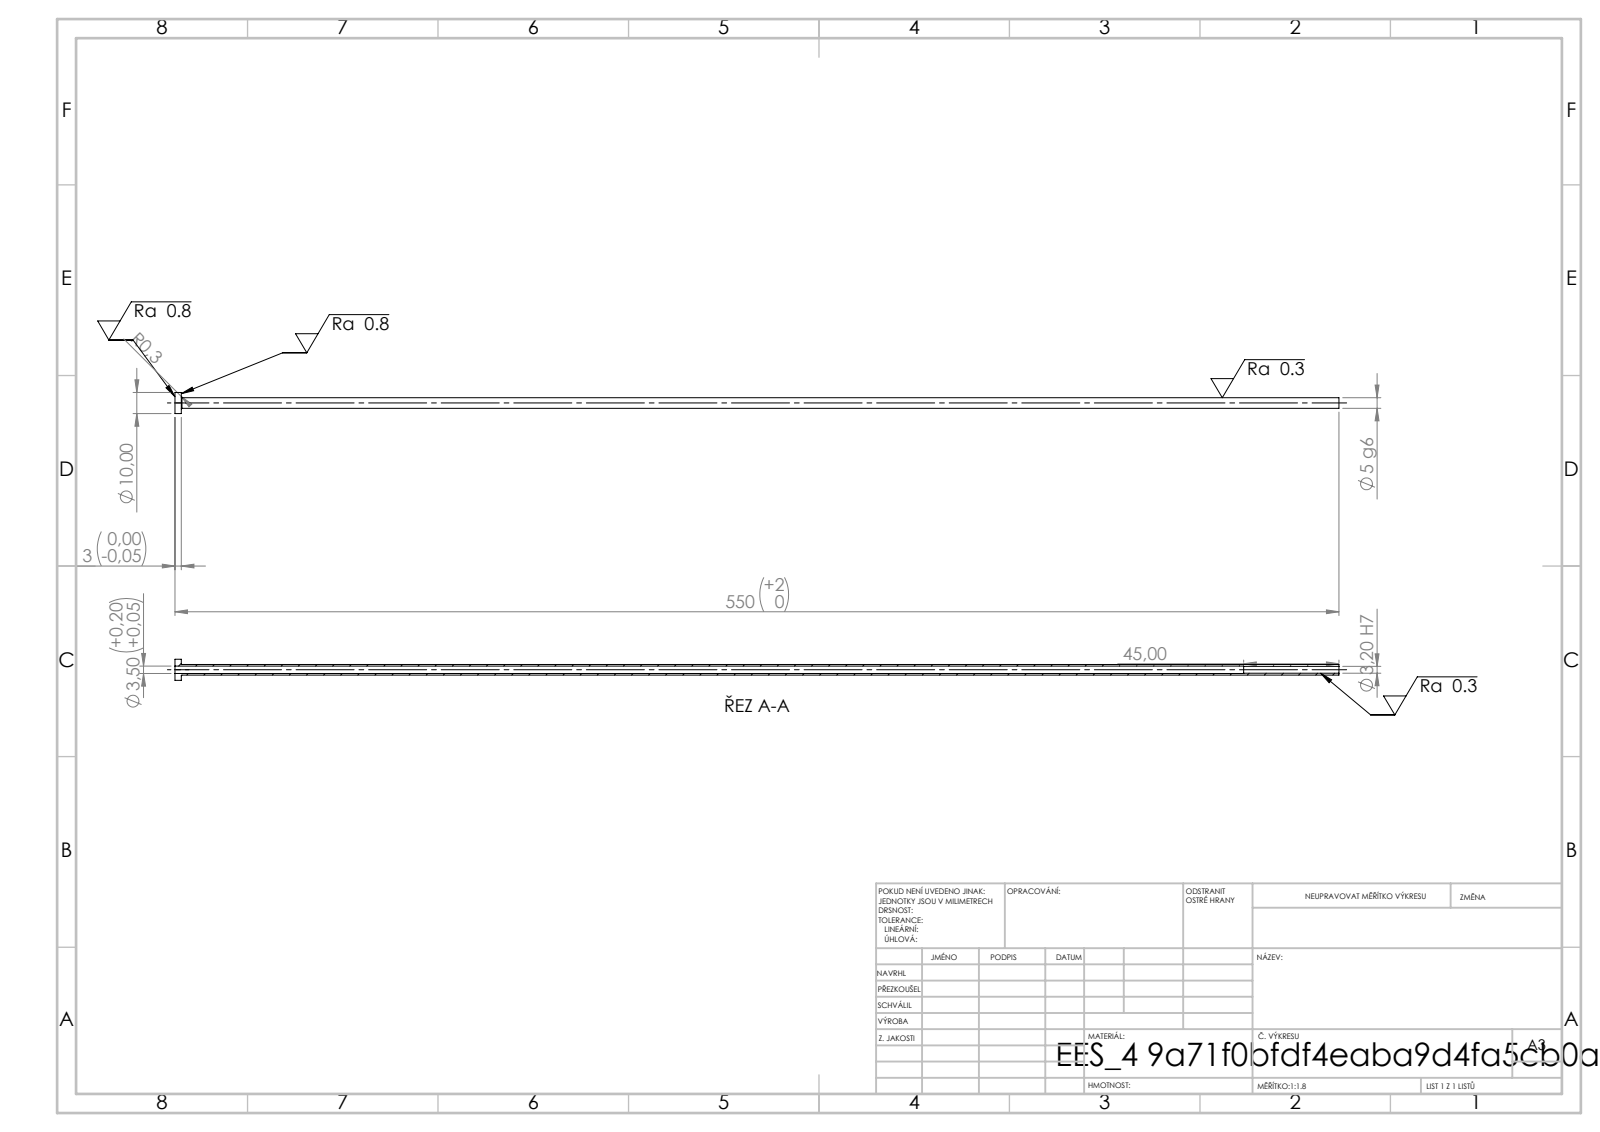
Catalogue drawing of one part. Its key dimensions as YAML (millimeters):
step_written_by: "SolidWorks 2019 (CONFIG_CONTROL_DESIGN)"
units: millimeters
bodies: {solids: 1, faces: 14, planar: 4, cylindrical: 8, other: 2}
overall_size: [550, 10, 10]
volume: 5756
surface_area: 14831
round_holes:
  - {diameter: 3.2, count: 1}
  - {diameter: 3.5, count: 1}
round_bosses_or_shafts:
  - {diameter: 10, count: 1}
  - {diameter: 5, count: 1}
face_to_face_distances: [3, 550, 547, 505, 502, 45]
